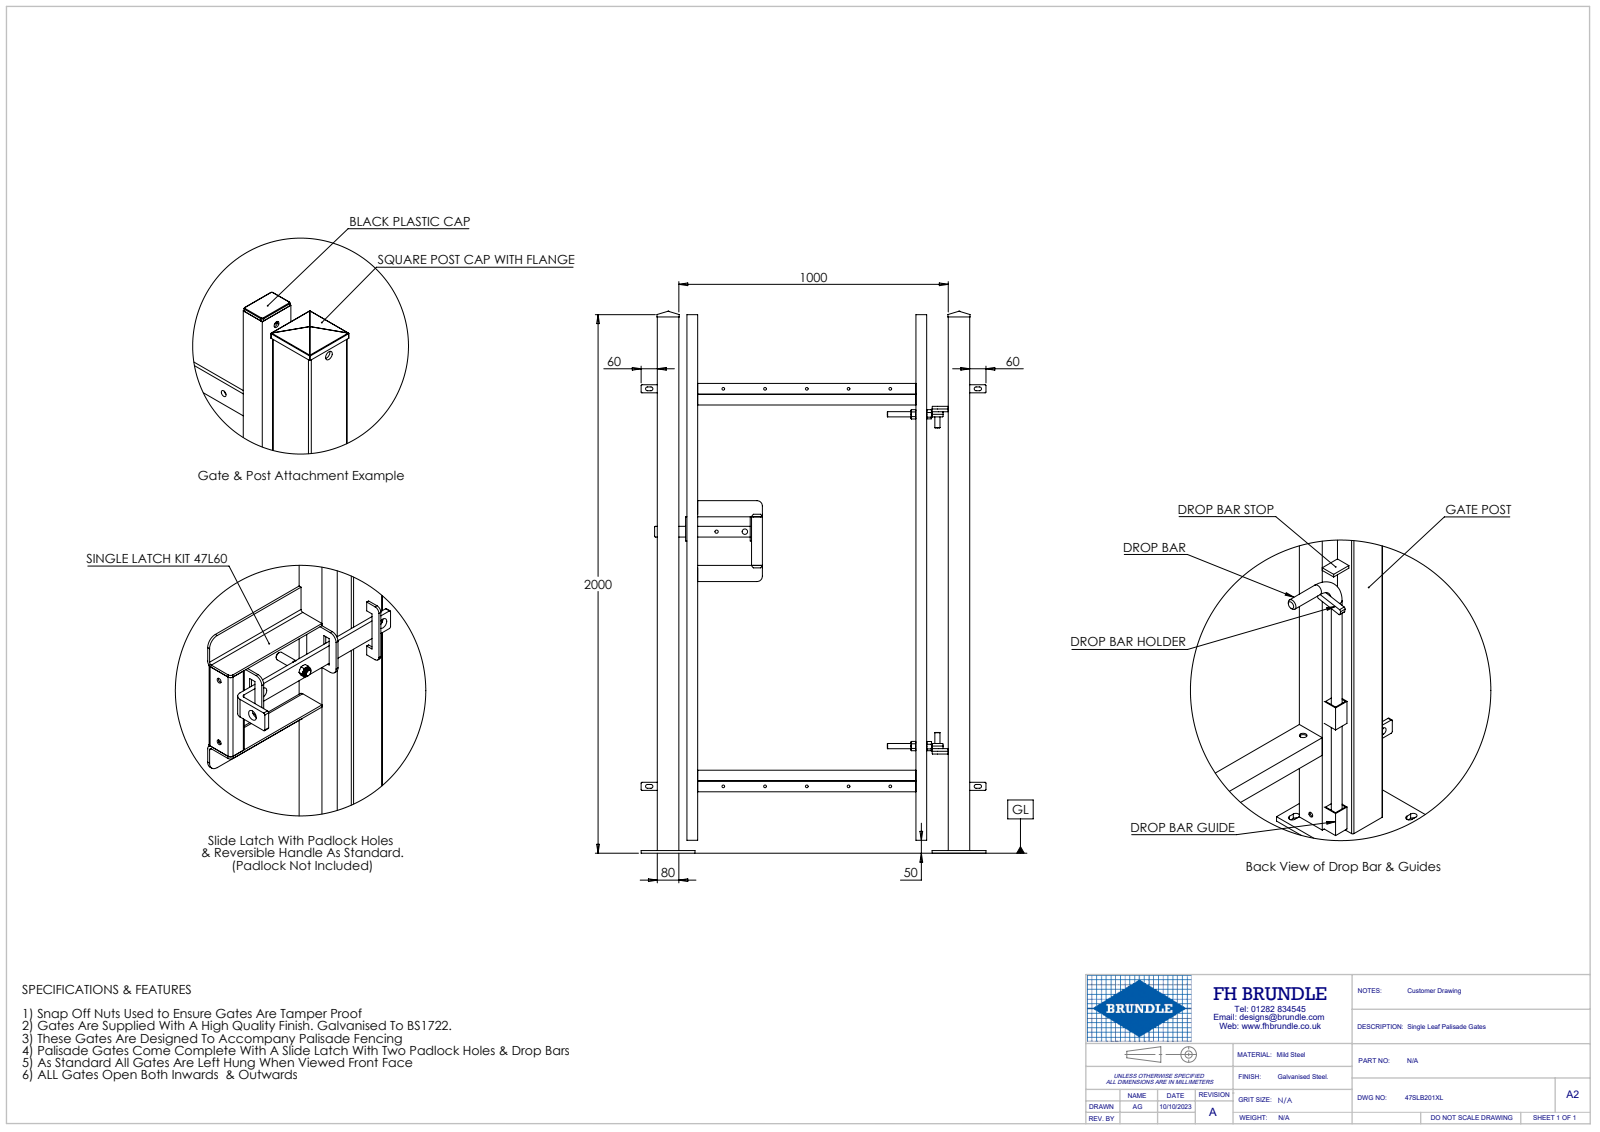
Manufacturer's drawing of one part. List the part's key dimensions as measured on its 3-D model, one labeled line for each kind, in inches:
Part name (STEP PRODUCT): 47SLB201XL Assem2_2000 x 1000 (Only Lugs); 05LUG6; 47SLB201XL Part5_(2.0 SINGLE); 47L60 Part3 (+8 more)
STEP written by: SolidWorks 2023 (CONFIG_CONTROL_DESIGN)
Units: inches
Bodies: 33 solids, 662 faces (324 planar, 238 cylindrical, 100 other)
Overall size (bounding box): 79.163 × 50.394 × 8.661
Volume: 681.6 in³ · Surface area: 8 009 in²
Round holes (diameter × count): ⌀0.394 ×14, ⌀0.787 ×7, ⌀0.551 ×3, ⌀0.689 ×2, ⌀0.709 ×2, ⌀0.472 ×1, ⌀0.827 ×1
Round bosses / shafts (diameter × count): ⌀0.748 ×3, ⌀1.181 ×2, ⌀0.764 ×2
Partial cylindrical surfaces — rounded edges, fillets, slot ends (radius × count): R0.276 ×24, R0.118 ×20, R0.02 ×16, R0.039 ×14, R0.126 ×4, R0.252 ×4, R0.591 ×3, R0.177 ×2
Main face-to-face distances: 0.197, 2.953, 2.756, 0.118, 3.15, 0.394, 1.457, 42.52, 2.559, 2.638
Hole centre spacings: 6.102, 58.391, 12.205, 59.339, 58.071, 18.307, 60.888, 0.02
